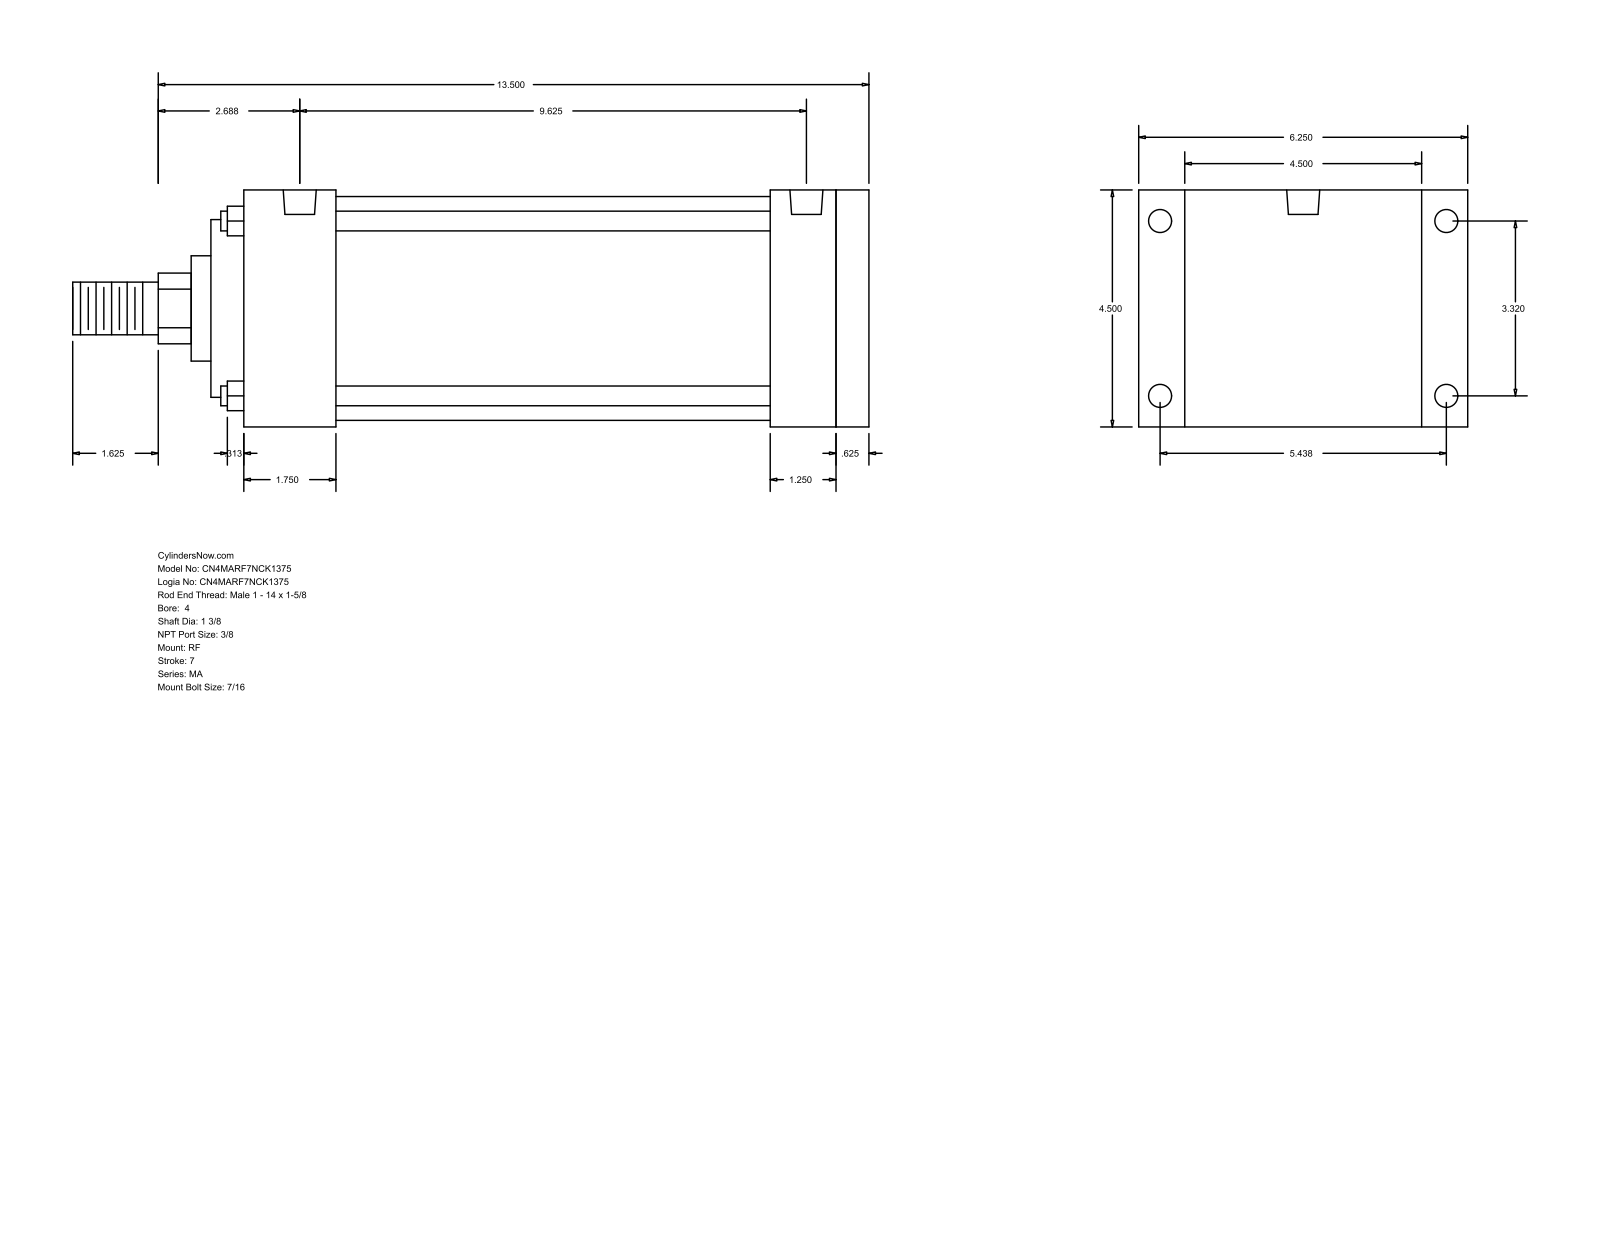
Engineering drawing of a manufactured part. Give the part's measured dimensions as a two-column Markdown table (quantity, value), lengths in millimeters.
| quantity | value |
| --- | --- |
| part name | MA_RF__0400_1.375 |
| STEP written by | GSSL Pune (CONFIG_CONTROL_DESIGN) |
| units | millimeters |
| bodies | 0 solids, 94 faces (65 planar, 29 cylindrical, 0 other) |
| overall size | 384.18 × 158.75 × 114.3 |
| round holes (diameter × count) | 11.11 × 8, 15.93 × 2 |
| round bosses / shafts (diameter × count) | 9.53 × 4, 107.95 × 1, 85.72 × 1, 50.8 × 1, 34.92 × 1, 25.4 × 1 |
| partial cylindrical surfaces (radius × count) | 17.06 × 1 |
| main face-to-face distances | 114.3, 301.63, 15.88, 285.75, 15.87, 301.62, 317.5, 22.23, 136.53, 269.87 |
| hole center spacings | 84.32, 138.12, 161.82, 234.95, 4.76, 4.77, 239.71, 239.72 |
